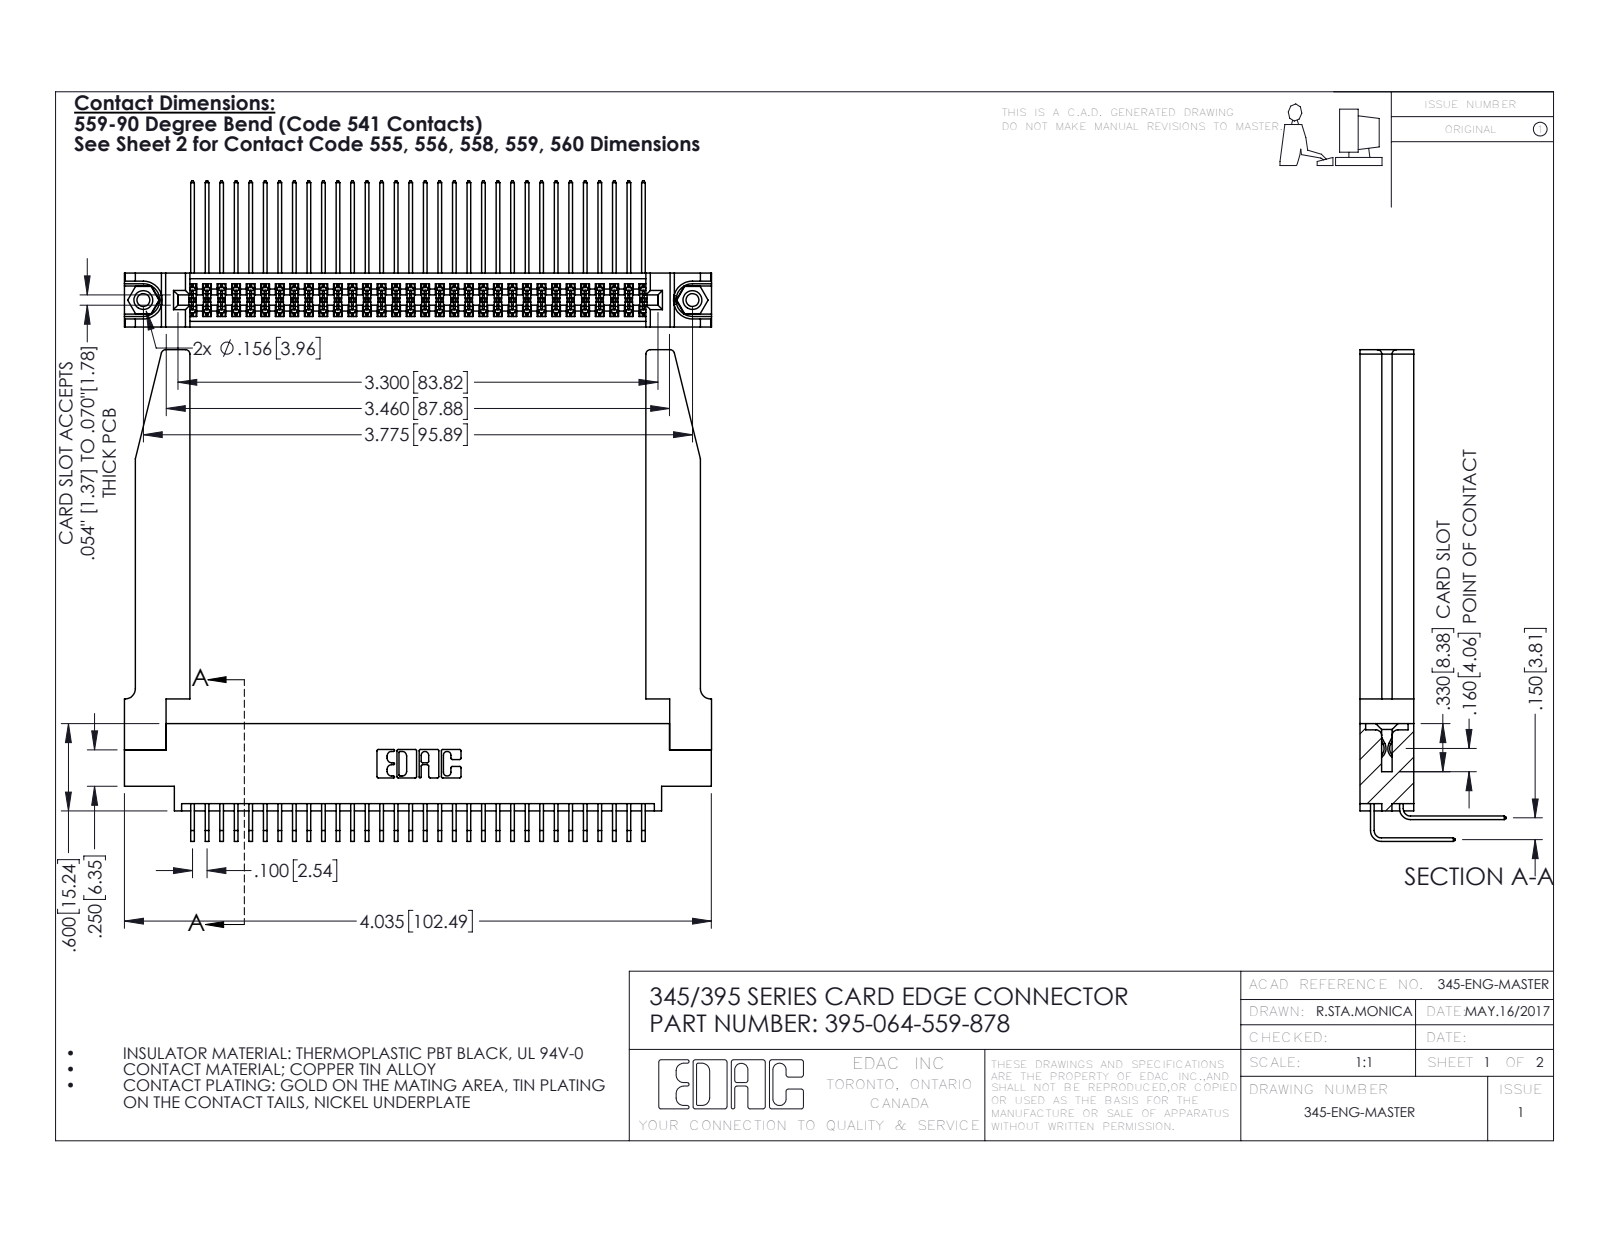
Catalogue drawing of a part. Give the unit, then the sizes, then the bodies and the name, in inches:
Units: inches
Overall size (bounding box): 4.036 × 3.379 × 1.005
Round holes (diameter × count): ⌀0.089 ×2, ⌀0.125 ×2, ⌀0.156 ×2, ⌀0.064 ×1
Round bosses / shafts (diameter × count): ⌀0.155 ×2
Partial cylindrical surfaces — rounded edges, fillets, slot ends (radius × count): R0.006 ×96, R0.01 ×22, R0.03 ×8, R0.007 ×6, R0.031 ×6, R0.026 ×3, R0.014 ×2, R0.019 ×2
Main face-to-face distances: 0.37, 0.072, 0.298, 0.098, 0.272, 0.025, 0.2, 0.225, 0.15, 0.175
Hole centre spacings: 0.27, 3.54, 3.775
Volume: 1.092 in³ · Surface area: 36.4 in²
Bodies: 69 solids, 3692 faces (2466 planar, 1174 cylindrical, 52 other)
Part name (STEP PRODUCT): 395-064-559-878; 345-292-001_558 559 Tail - 1; 345-220-078_345-220-078; 345 Part_0.170 Offset - 0.156 Dia-TH (+2 more)
STEP written by: SolidWorks 2016 (CONFIG_CONTROL_DESIGN)
